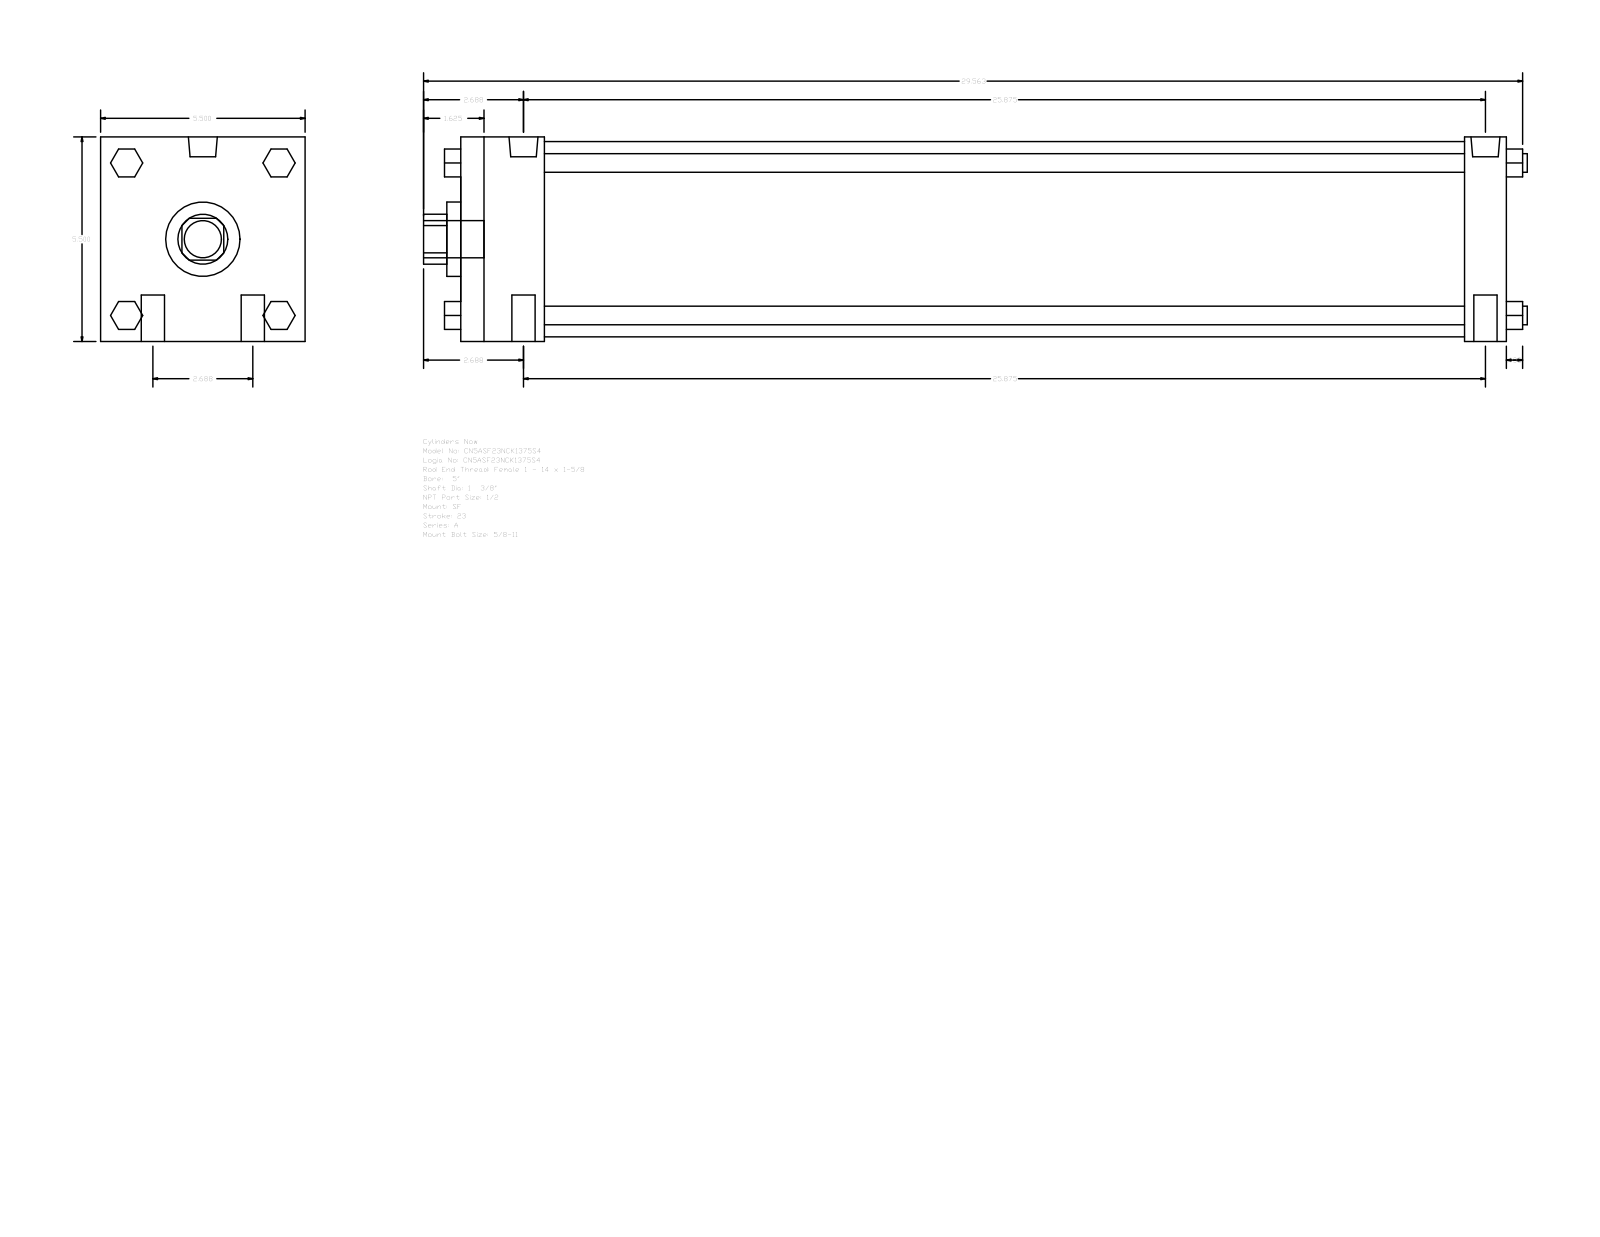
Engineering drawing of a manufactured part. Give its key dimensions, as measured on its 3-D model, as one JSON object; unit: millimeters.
{"part_name": "A_SF__0500_1.375", "step_written_by": "GSSL Pune (CONFIG_CONTROL_DESIGN)", "units": "millimeters", "bodies": {"solids": 0, "faces": 124, "planar": 94, "cylindrical": 30, "other": 0}, "overall_size": [754.06, 139.7, 139.7], "round_holes": [[34.92, 1], [50.8, 1], [133.35, 1]], "round_bosses_or_shafts": [[15.88, 4], [12.7, 4], [19.77, 2], [8.73, 2], [25.4, 1]], "partial_cylinders_radius": [[17.06, 1]], "face_to_face_distances": [139.7, 714.37, 28.57, 57.15, 685.8, 628.65, 657.22, 19.05, 52.07, 90.18]}
